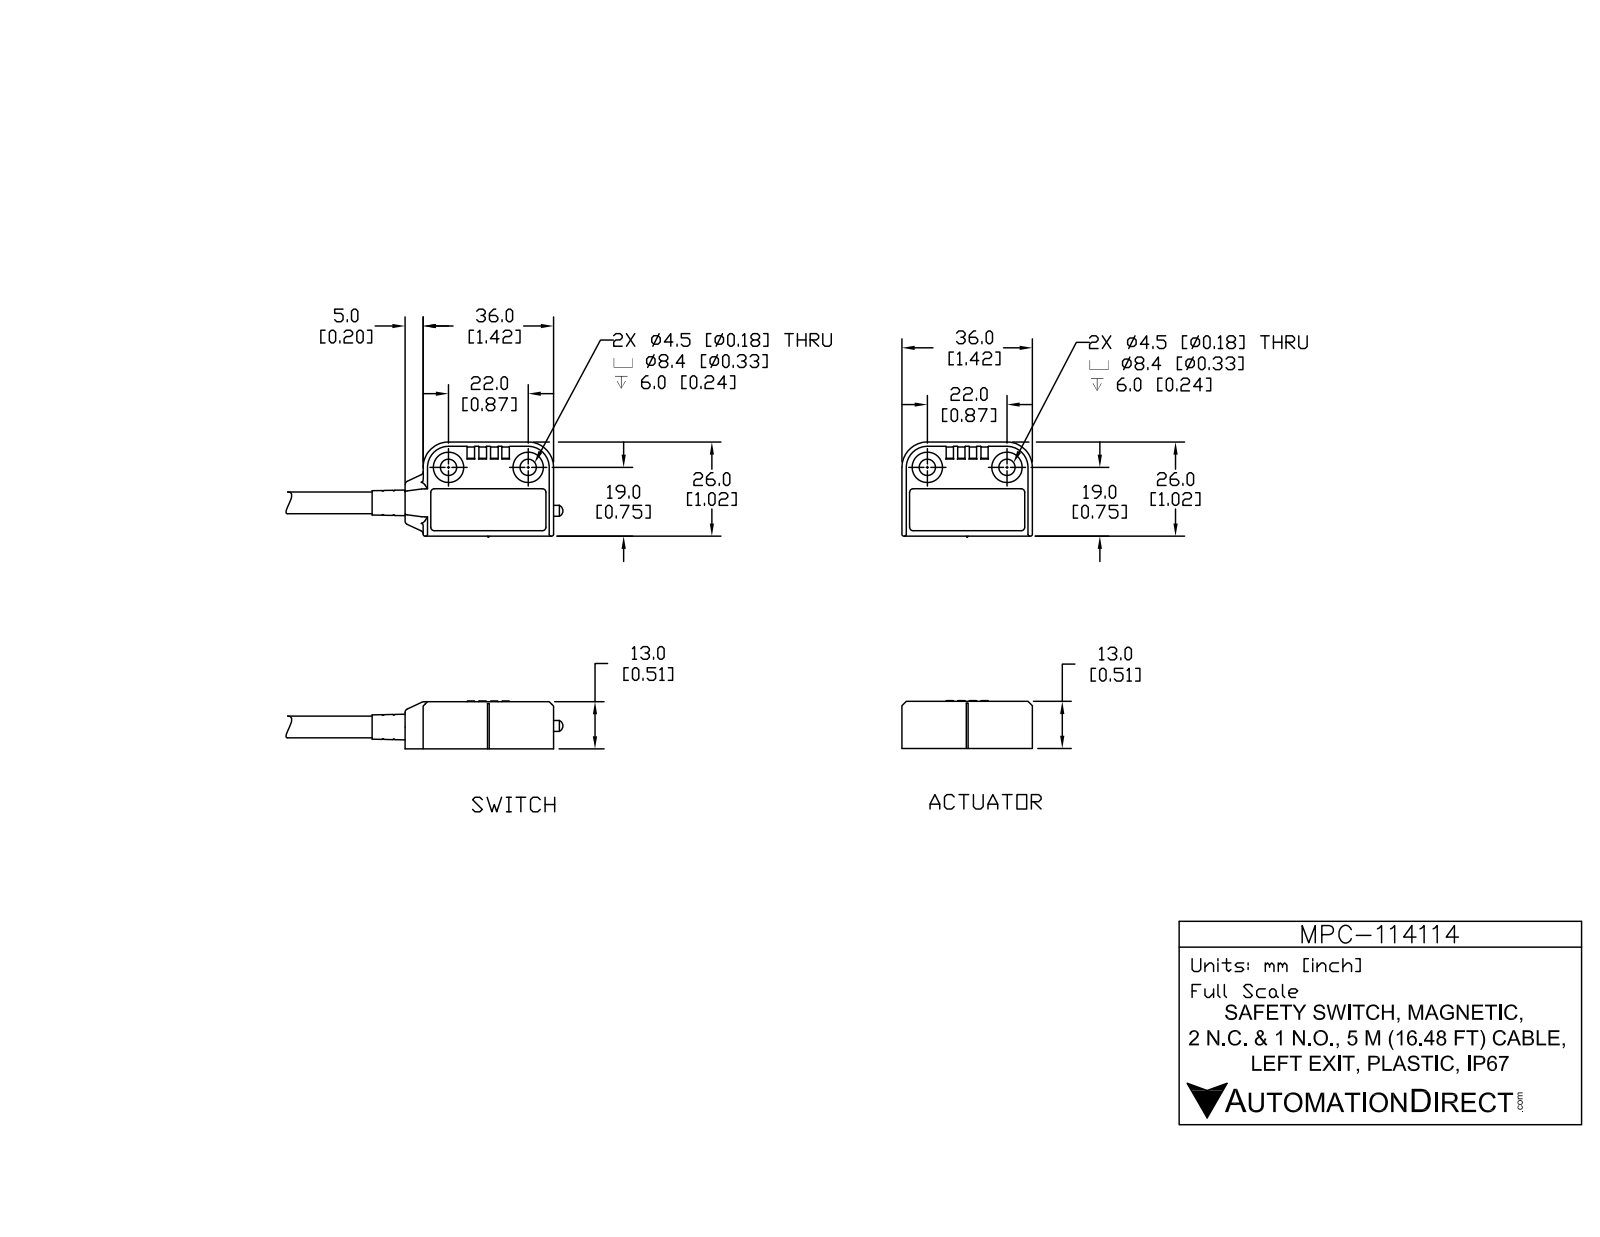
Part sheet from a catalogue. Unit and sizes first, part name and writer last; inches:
Units: inches
Overall size (bounding box): 7.748 × 2.087 × 0.528
Round holes (diameter × count): ⌀0.177 ×4, ⌀0.331 ×4, ⌀0.195 ×2, ⌀0.098 ×1, ⌀0.118 ×1, ⌀0.197 ×1, ⌀0.232 ×1, ⌀0.244 ×1, ⌀0.291 ×1
Round bosses / shafts (diameter × count): ⌀0.236 ×2, ⌀0.197 ×2, ⌀0.091 ×2, ⌀0.079 ×2, ⌀0.031 ×2, ⌀0.339 ×1, ⌀0.299 ×1, ⌀0.28 ×1
Partial cylindrical surfaces — rounded edges, fillets, slot ends (radius × count): R0.02 ×84, R0.012 ×32, R0.008 ×30, R0.004 ×17, R0.039 ×13, R0.169 ×4, R0.201 ×4, R0.276 ×4
Main face-to-face distances: 0.055, 0.508, 0.449, 0.461, 0.059, 0.047, 1.063, 0.496, 0.445, 0.031
Hole centre spacings: 0.866, 0.434, 0.445, 0.974, 1.091, 1.152, 1.393, 1.535
Volume: 1.065 in³ · Surface area: 29.75 in²
Bodies: 10 solids, 1067 faces (453 planar, 346 cylindrical, 268 other)
Part name (STEP PRODUCT): MPC-114114; MPC-114114_2; MPC-114114_1
STEP written by: SolidWorks 2017 (AUTOMOTIVE_DESIGN)
